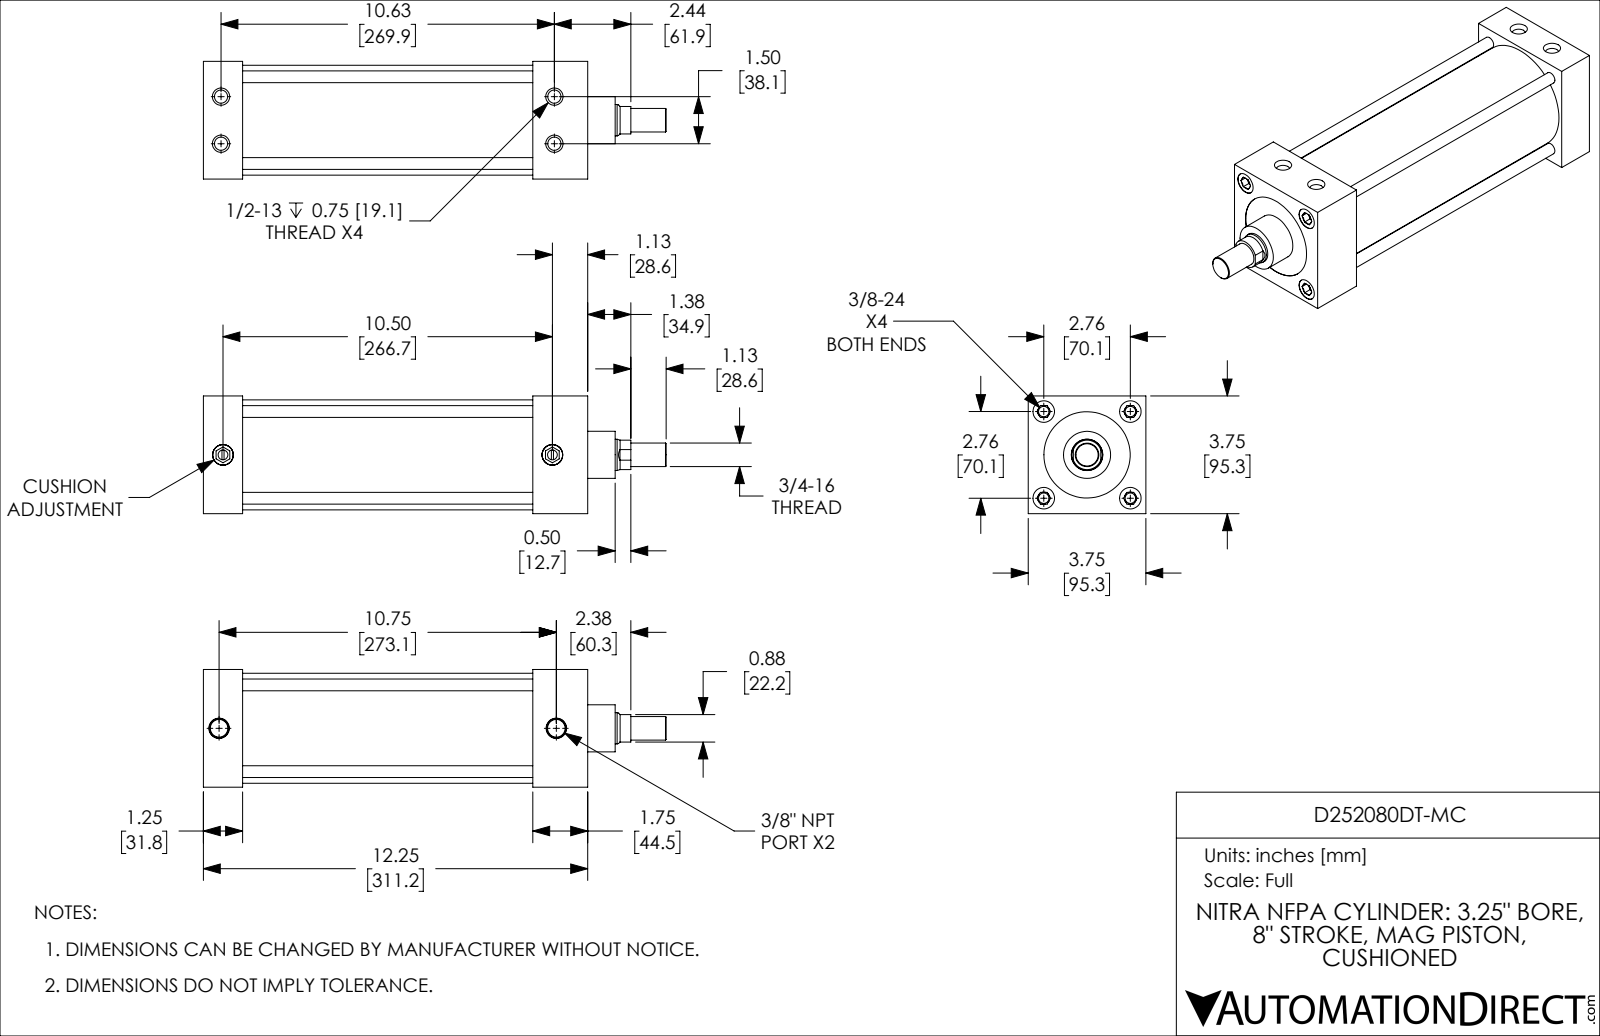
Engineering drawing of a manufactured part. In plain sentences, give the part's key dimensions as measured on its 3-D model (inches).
The part is named "D252080DT-MC; D252080DT-MC_CUSHION; D252080DT-MC_PISTON_KK1; D252080DT-MC_BODY". Its 3-D file was written by "SolidWorks 2019 (CONFIG_CONTROL_DESIGN)". It is 4 solids with 246 faces: 90 planar, 78 cylindrical and 78 other. Overall it measures 14.75 by 3.75 by 3.75 inches. Its volume is 75.22 cubic inches and its surface area 438.2 square inches. Round holes: 4 of diameter 0.332, 4 of diameter 0.422, 4 of diameter 0.687, 2 of diameter 0.312, 2 of diameter 0.562, 2 of diameter 0.656, 1 of diameter 1.001, 1 of diameter 2.75, 1 of diameter 3.251. Round bosses or shafts: 4 of diameter 0.375, 2 of diameter 0.657, 1 of diameter 3.501, 1 of diameter 3.249, 1 of diameter 1.5, 1 of diameter 0.999, 1 of diameter 0.75. Partial cylindrical surfaces (rounded edges, fillets, slot ends): 1 of radius 0.469. The main face-to-face distances are 1.25, 3.75, 10.5, 9.25, 2.5, 8, 12.25, 11, 9.75, 1.75. The hole center spacings are 0.753, 1.952, 2.76, 10.714, 1.5, 3.903, 10.625, 10.73.
